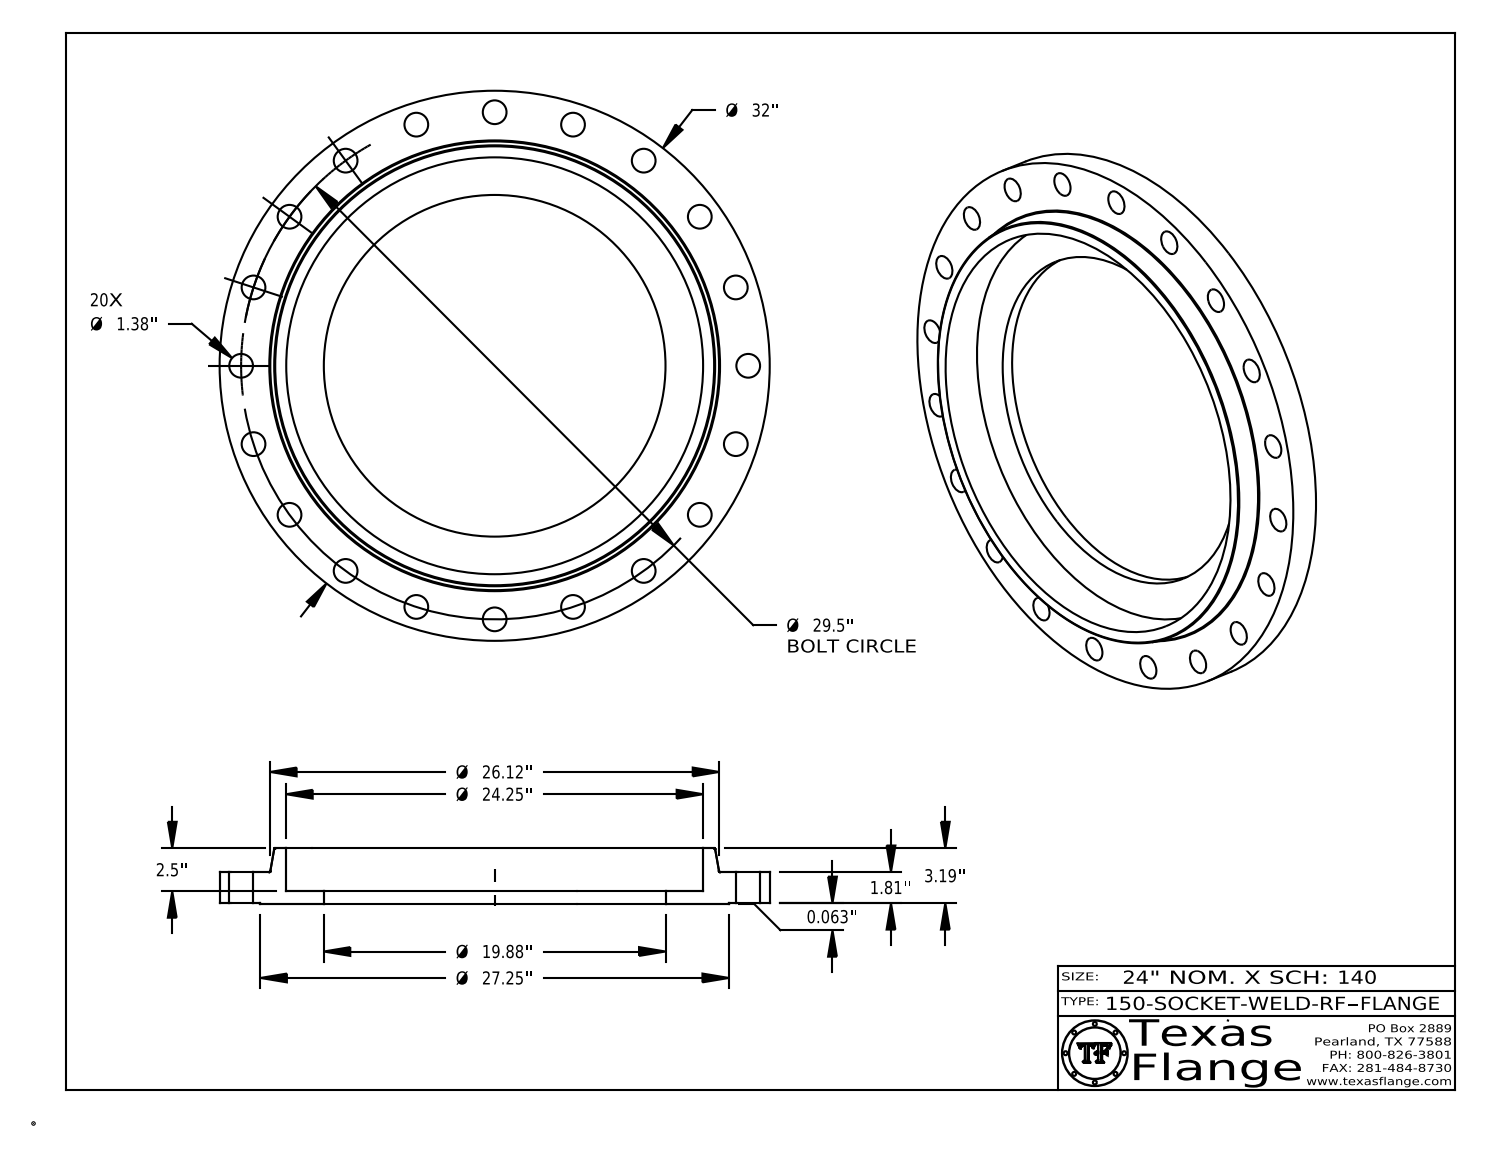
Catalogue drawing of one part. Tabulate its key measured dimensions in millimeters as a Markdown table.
| quantity | value |
| --- | --- |
| part name | 150-SOCKET-WELD-RF |
| STEP written by | CATIA V5 STEP AP214 (AUTOMOTIVE_DESIGN) |
| units | millimeters |
| bodies | 1 solid, 444 faces (370 planar, 68 cylindrical, 6 other) |
| overall size | 812.8 × 812.8 × 82.6 |
| volume | 12 710 000 mm³ |
| surface area | 1 033 000 mm² |
| round holes (diameter × count) | 35.1 × 20, 12.6 × 1, 504.9 × 1, 616 × 1 |
| round bosses / shafts (diameter × count) | 0.8 × 8, 812.8 × 1, 692.2 × 1, 9.9 × 1 |
| main face-to-face distances | 47.5, 1.6, 46, 19.1, 17.5, 28.4, 82.6, 81, 63.5, 35.1 |
| hole center spacings | 374.7, 740.1, 117.2, 440.4, 529.8, 606.2, 667.6, 231.5 |
